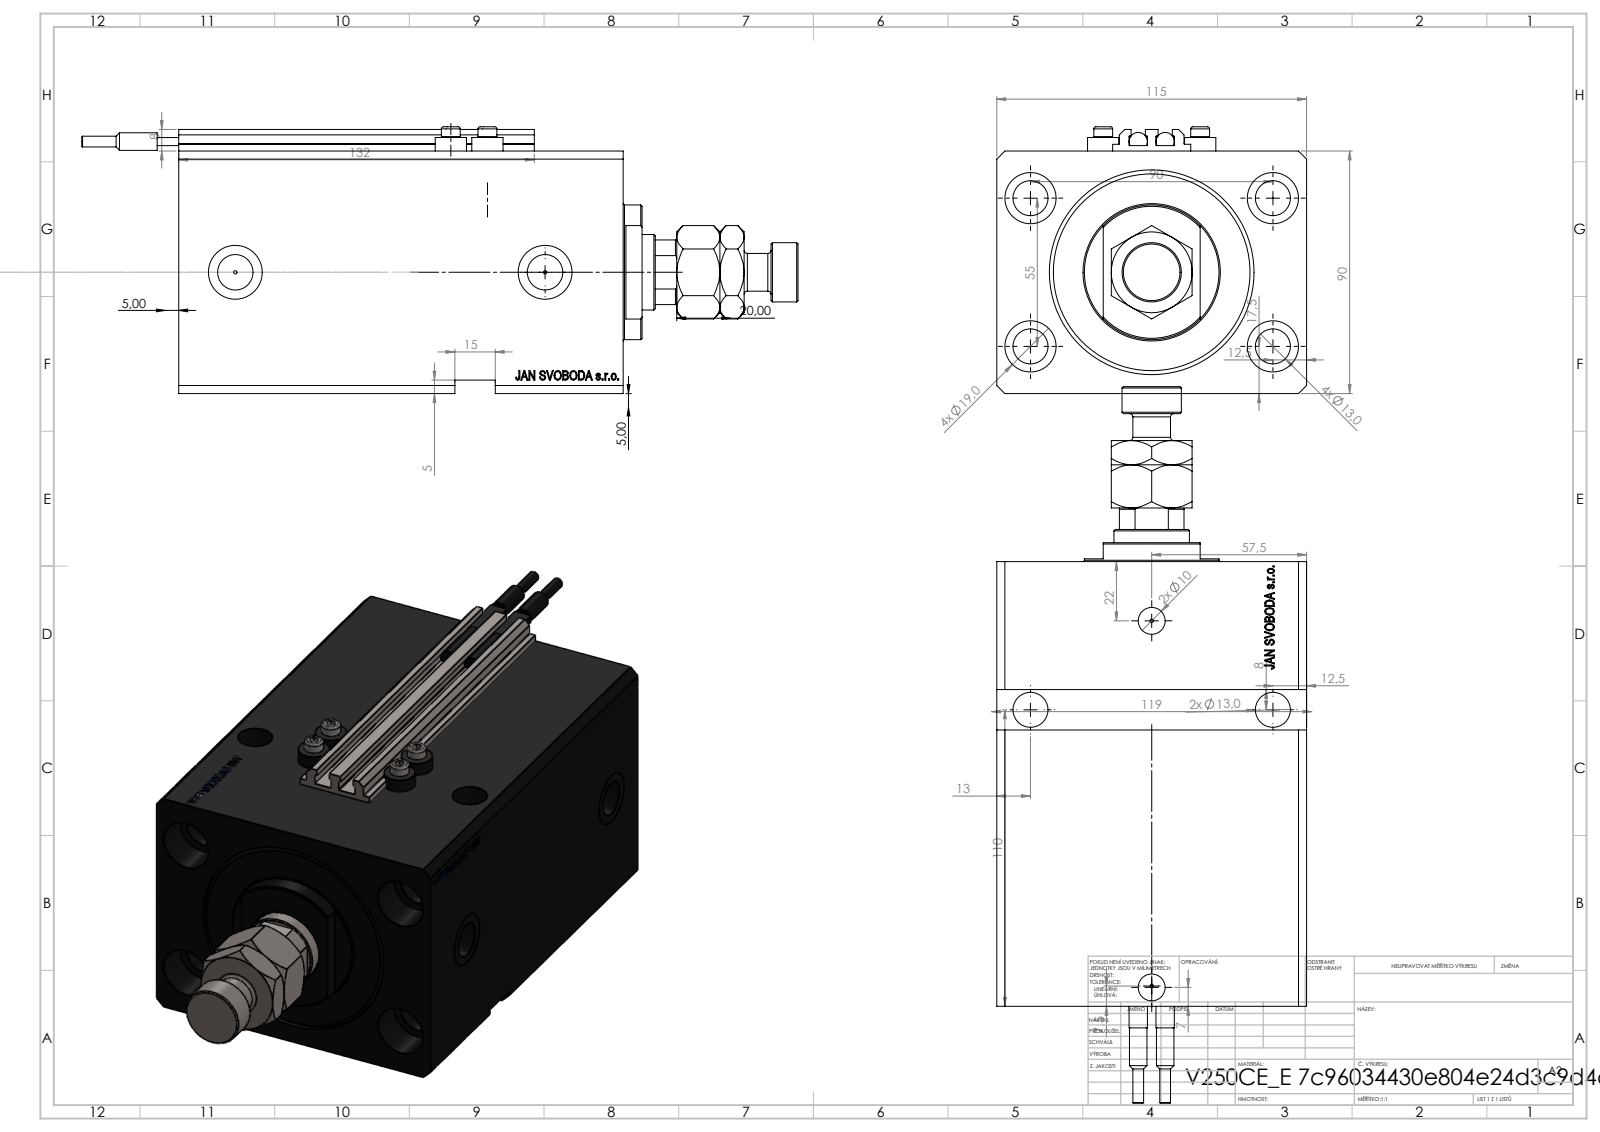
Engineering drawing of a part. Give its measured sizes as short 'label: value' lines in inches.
name: V250CE_E_Body; ALLEN BOLT V250CE; V250CE_VC_E; SWITCH_V250CE (+2 more)
written by: SolidWorks 2019 (CONFIG_CONTROL_DESIGN)
unit: in
bodies: 11 solids, 1235 faces (595 planar, 162 cylindrical, 478 other)
size: 10.472 × 4.528 × 3.898
volume: 86.59 in³; area: 345.5 in²
holes: 6× ⌀0.512, 4× ⌀0.049, 4× ⌀0.157, 4× ⌀0.748, 2× ⌀0.335, 2× ⌀0.394, 2× ⌀0.518, 2× ⌀0.787, 1× ⌀0.728, 1× ⌀1.102, 1× ⌀2.48, 1× ⌀2.992
bosses: 4× ⌀0.457, 4× ⌀0.276, 2× ⌀0.268, 2× ⌀0.256, 2× ⌀0.157, 1× ⌀1.969, 1× ⌀0.866, 1× ⌀0.551
rounds: 10× R0.008, 1× R0.531
face distances: 3.543, 4.528, 0.787, 6.496, 0.705, 5.791, 5.709, 5.004, 2.559, 0.512
hole spacings: 2.076, 3.543, 0.535, 0.581, 1.078, 1.083, 1.12, 1.17
